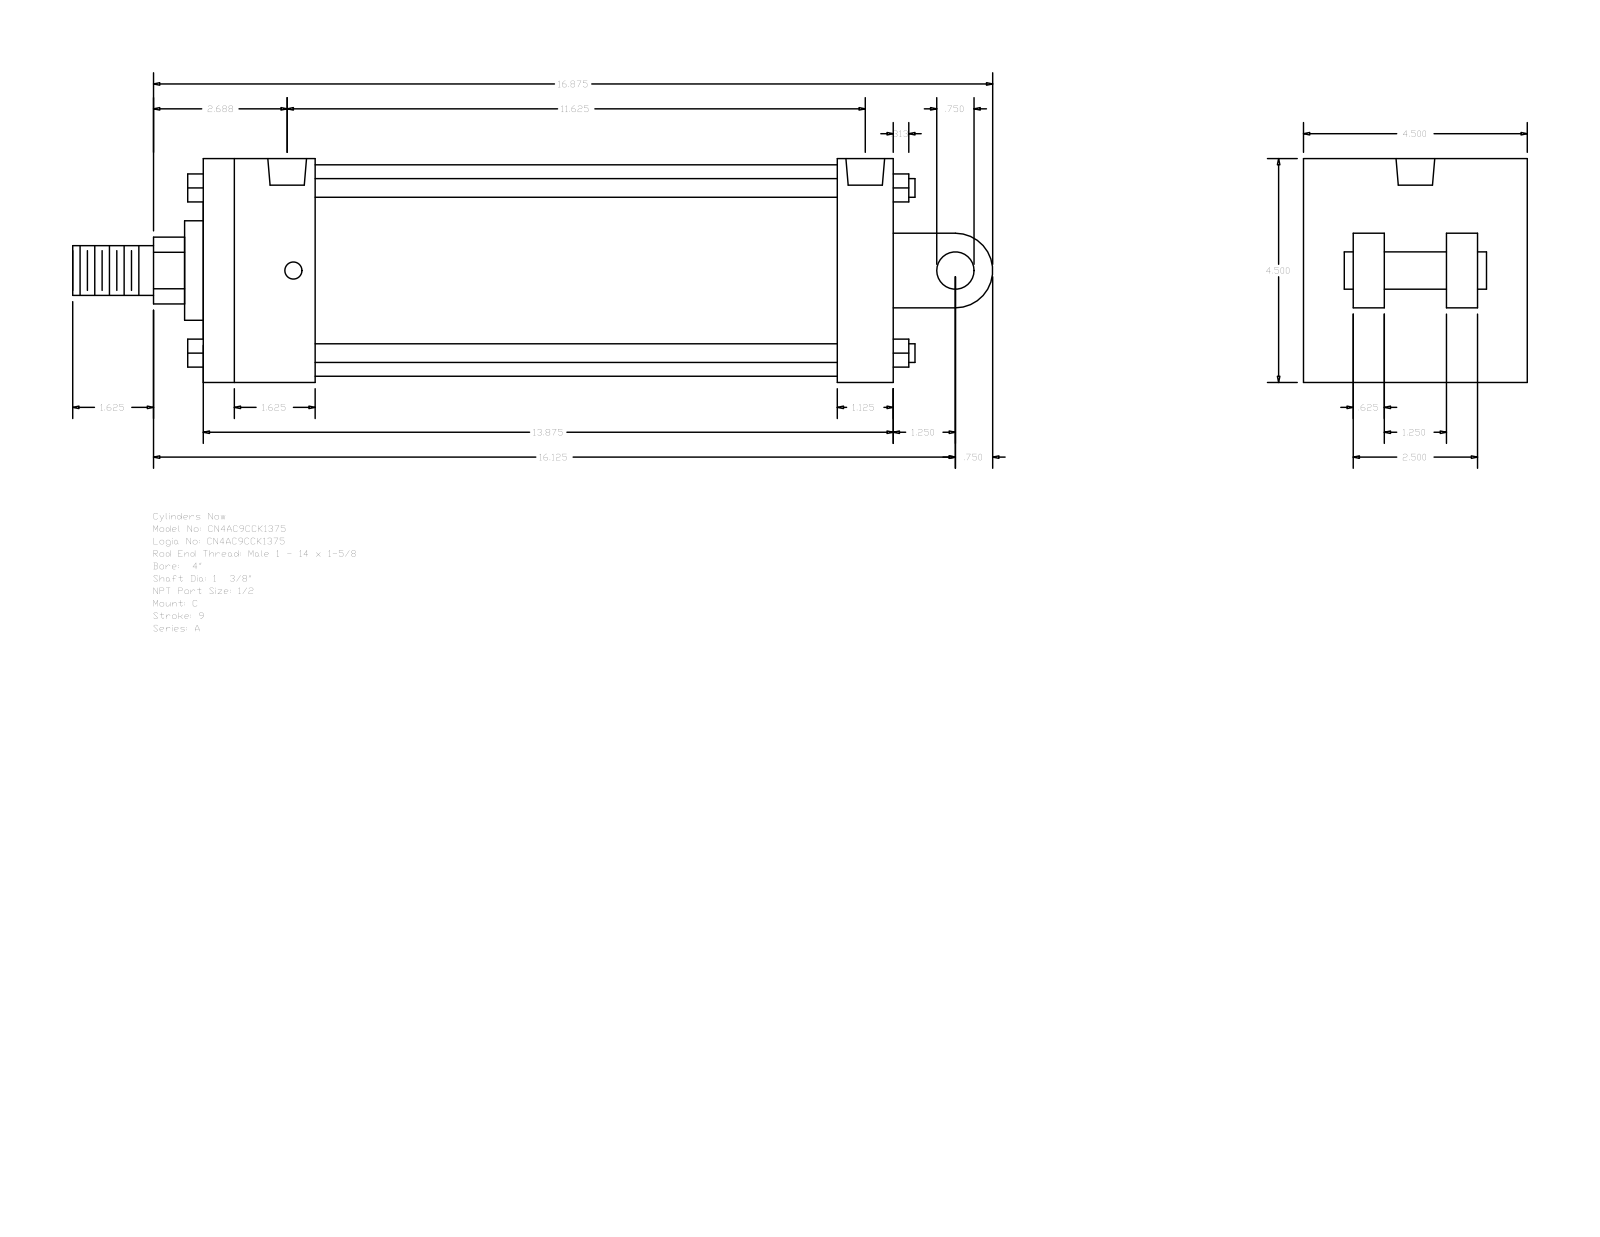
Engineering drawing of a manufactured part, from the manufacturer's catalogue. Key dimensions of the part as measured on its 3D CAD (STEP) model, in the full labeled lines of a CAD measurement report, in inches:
Part name (STEP PRODUCT): A_C__0400_1.375
STEP written by: GSSL Pune (CONFIG_CONTROL_DESIGN)
Units: inches
Bodies: 0 solids, 135 faces (102 planar, 33 cylindrical, 0 other)
Overall size (bounding box): 18.5 × 4.5 × 4.5
Round holes (diameter × count): ⌀0.344 ×4, ⌀0.778 ×2
Round bosses / shafts (diameter × count): ⌀0.375 ×4, ⌀4.25 ×1, ⌀2 ×1, ⌀1.375 ×1, ⌀1 ×1, ⌀0.75 ×1
Partial cylindrical surfaces — rounded edges, fillets, slot ends (radius × count): R0.672 ×1, R0.75 ×1
Main face-to-face distances: 4.5, 13.875, 2.25, 2.875, 12.75, 1.125, 10.5, 11.625, 1.625, 1
Hole centre spacings: 0.125, 11.375, 11.5, 11.625
